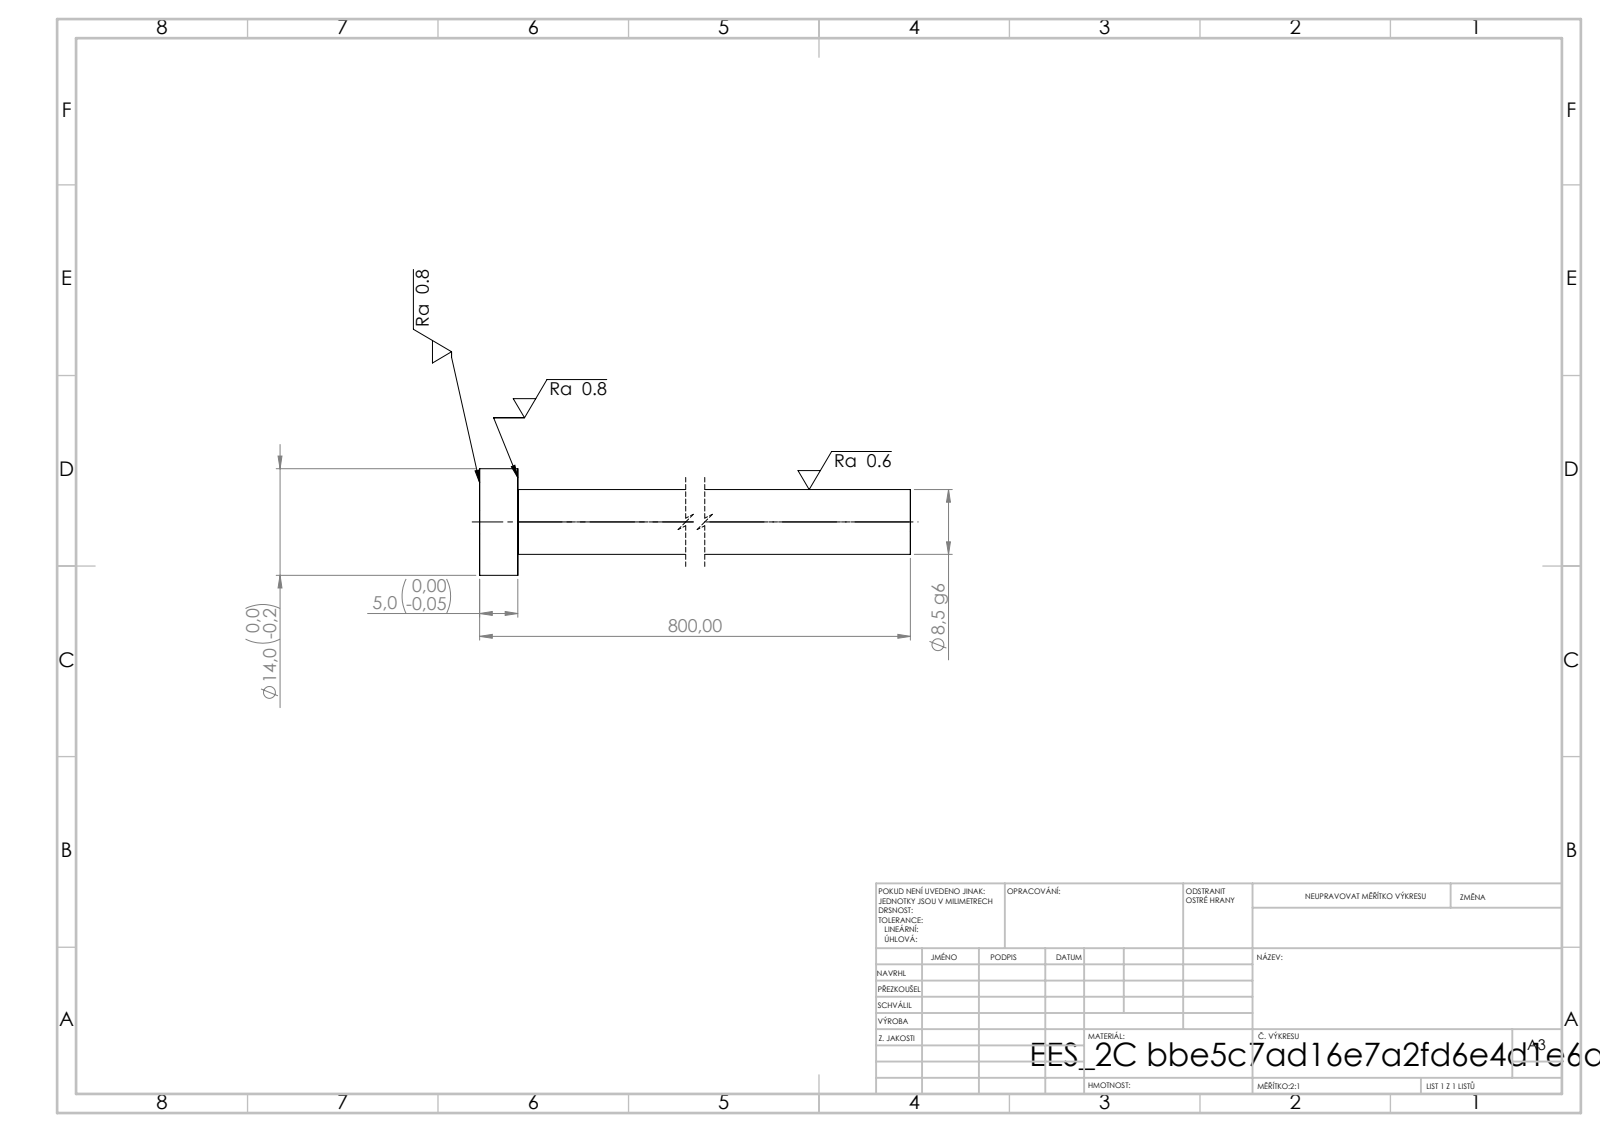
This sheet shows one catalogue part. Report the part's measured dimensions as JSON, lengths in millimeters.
{"step_written_by": "SolidWorks 2019 (CONFIG_CONTROL_DESIGN)", "units": "millimeters", "bodies": {"solids": 1, "faces": 7, "planar": 3, "cylindrical": 4, "other": 0}, "overall_size": [800, 14, 14], "volume_mm3": 45882, "surface_area_mm2": 21757, "round_bosses_or_shafts": [[14, 1], [8.5, 1]], "face_to_face_distances": [5, 800, 795]}
